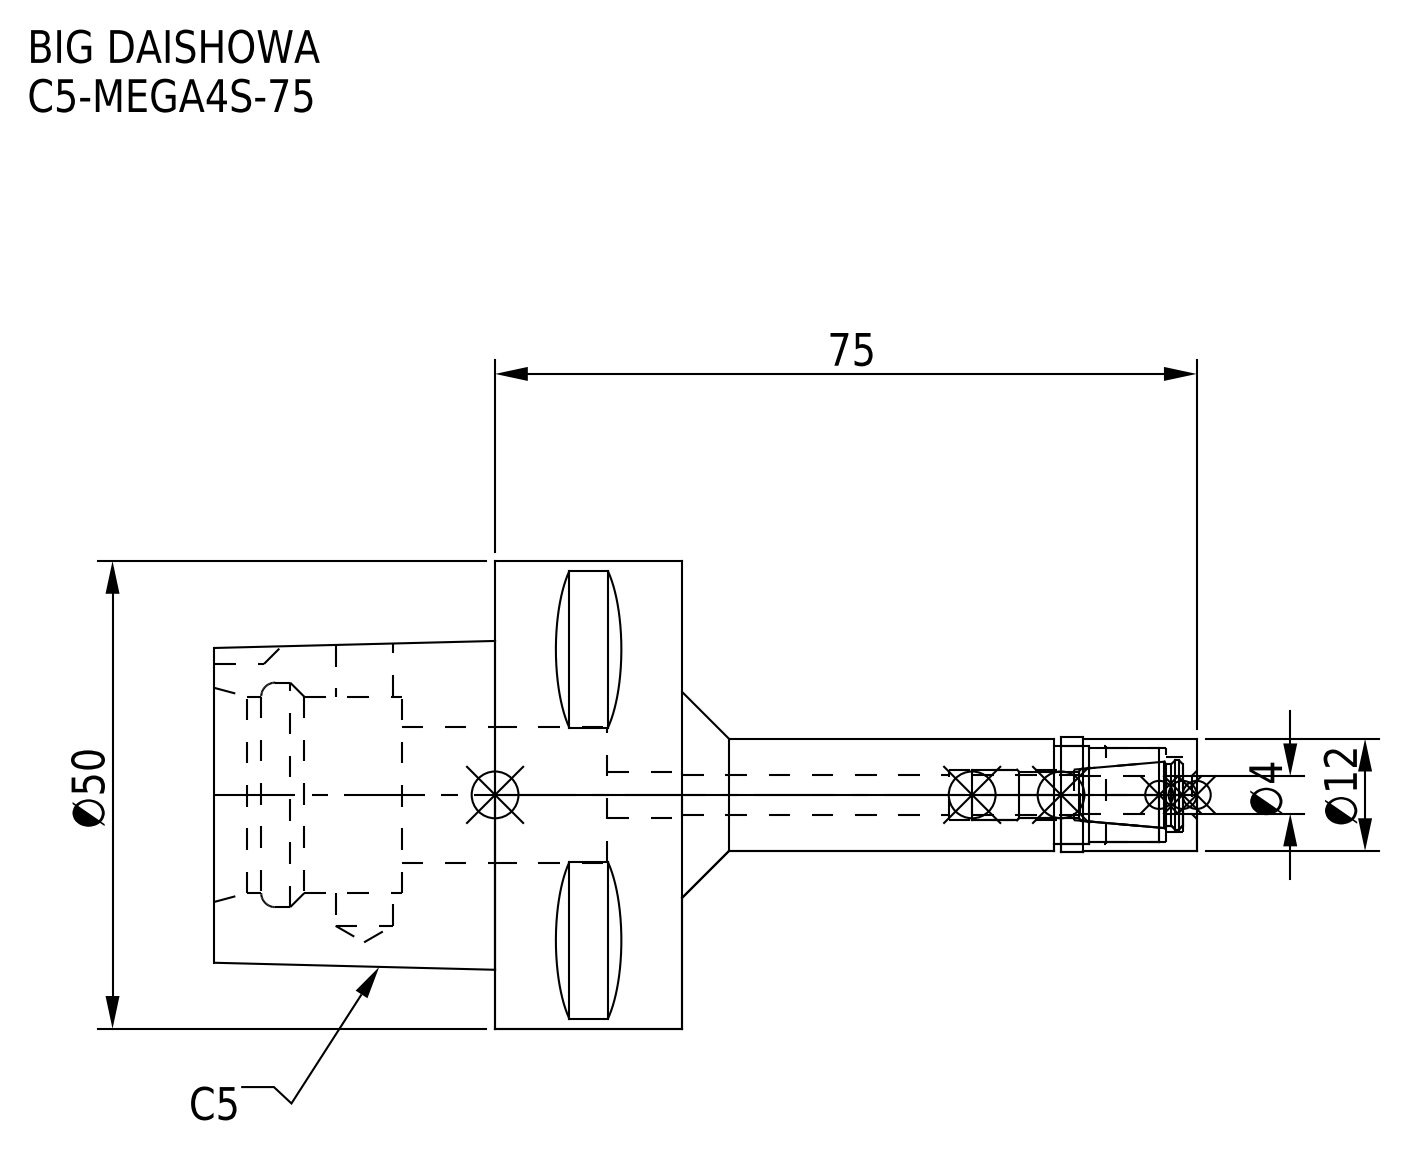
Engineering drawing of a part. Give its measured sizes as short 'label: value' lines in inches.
name: C5-MEGA4S-75_1.stp; C5-MEGA4S-75-040_ASM.stp; MGN4S_1.stp; DXF_TEMP_ASSY_ASM_4_ASM.stp (+3 more)
written by: SolidWorks 2019 (CONFIG_CONTROL_DESIGN)
unit: in
bodies: 2 solids, 93 faces (38 planar, 39 cylindrical, 16 other)
size: 4.134 × 1.969 × 1.969
volume: 3.661 in³; area: 26.03 in²
holes: 1× ⌀0.161, 1× ⌀0.165, 1× ⌀0.197, 1× ⌀0.213, 1× ⌀0.24, 1× ⌀0.315, 1× ⌀0.394, 1× ⌀0.413, 1× ⌀0.571, 1× ⌀0.827, 1× ⌀0.945
bosses: 1× ⌀1.969, 1× ⌀0.484, 1× ⌀0.472
rounds: 1× R0.157
face distances: 0.787, 1.181, 1.969, 1.732, 0.394, 0.472, 0.755, 0.315, 0.866, 1.654
